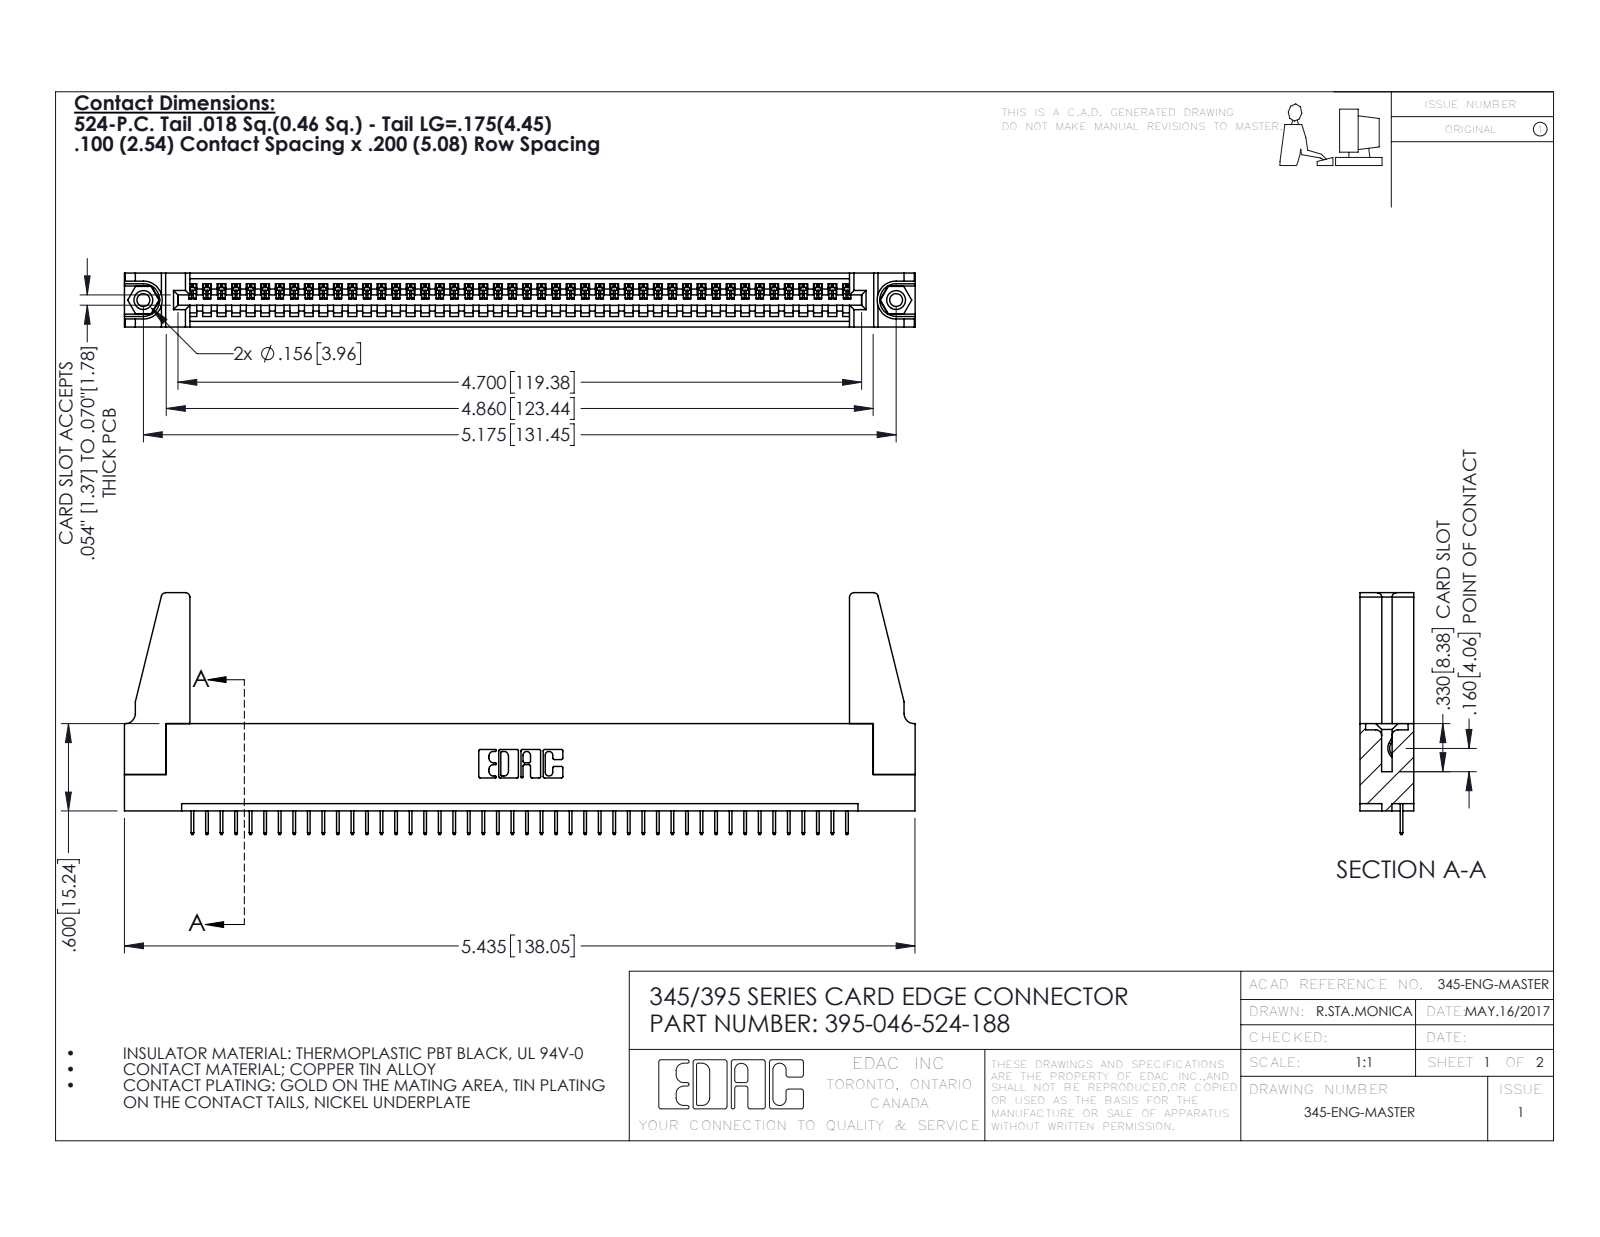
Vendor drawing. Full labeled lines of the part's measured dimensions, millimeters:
Part name (STEP PRODUCT): 345-292-001_345-293-124; 345-250-001_345-250-001-102; 345 Part_Flush Mounting Lugs - 0.156 Dia-TH; 395-046-524-188 (+1 more)
STEP written by: SolidWorks 2016 (CONFIG_CONTROL_DESIGN)
Units: millimetres
Bodies: 51 solids, 3102 faces (2268 planar, 818 cylindrical, 16 other)
Overall size (bounding box): 138.1 × 42.2 × 9.4
Volume: 16 200 mm³ · Surface area: 19 830 mm²
Round holes (diameter × count): ⌀2.3 ×2, ⌀3.2 ×2, ⌀4 ×2, ⌀1.6 ×1
Round bosses / shafts (diameter × count): ⌀3.9 ×2
Partial cylindrical surfaces — rounded edges, fillets, slot ends (radius × count): R0.2 ×92, R0.3 ×22, R0.8 ×8, R0.2 ×6, R0.8 ×6, R0.7 ×3, R0.8 ×2, R1 ×2
Main face-to-face distances: 1.8, 9.4, 7.6, 5.1, 2.5, 6.9, 0.6, 5.7, 1.8, 3.8
Hole centre spacings: 6.9, 125.5, 131.4
